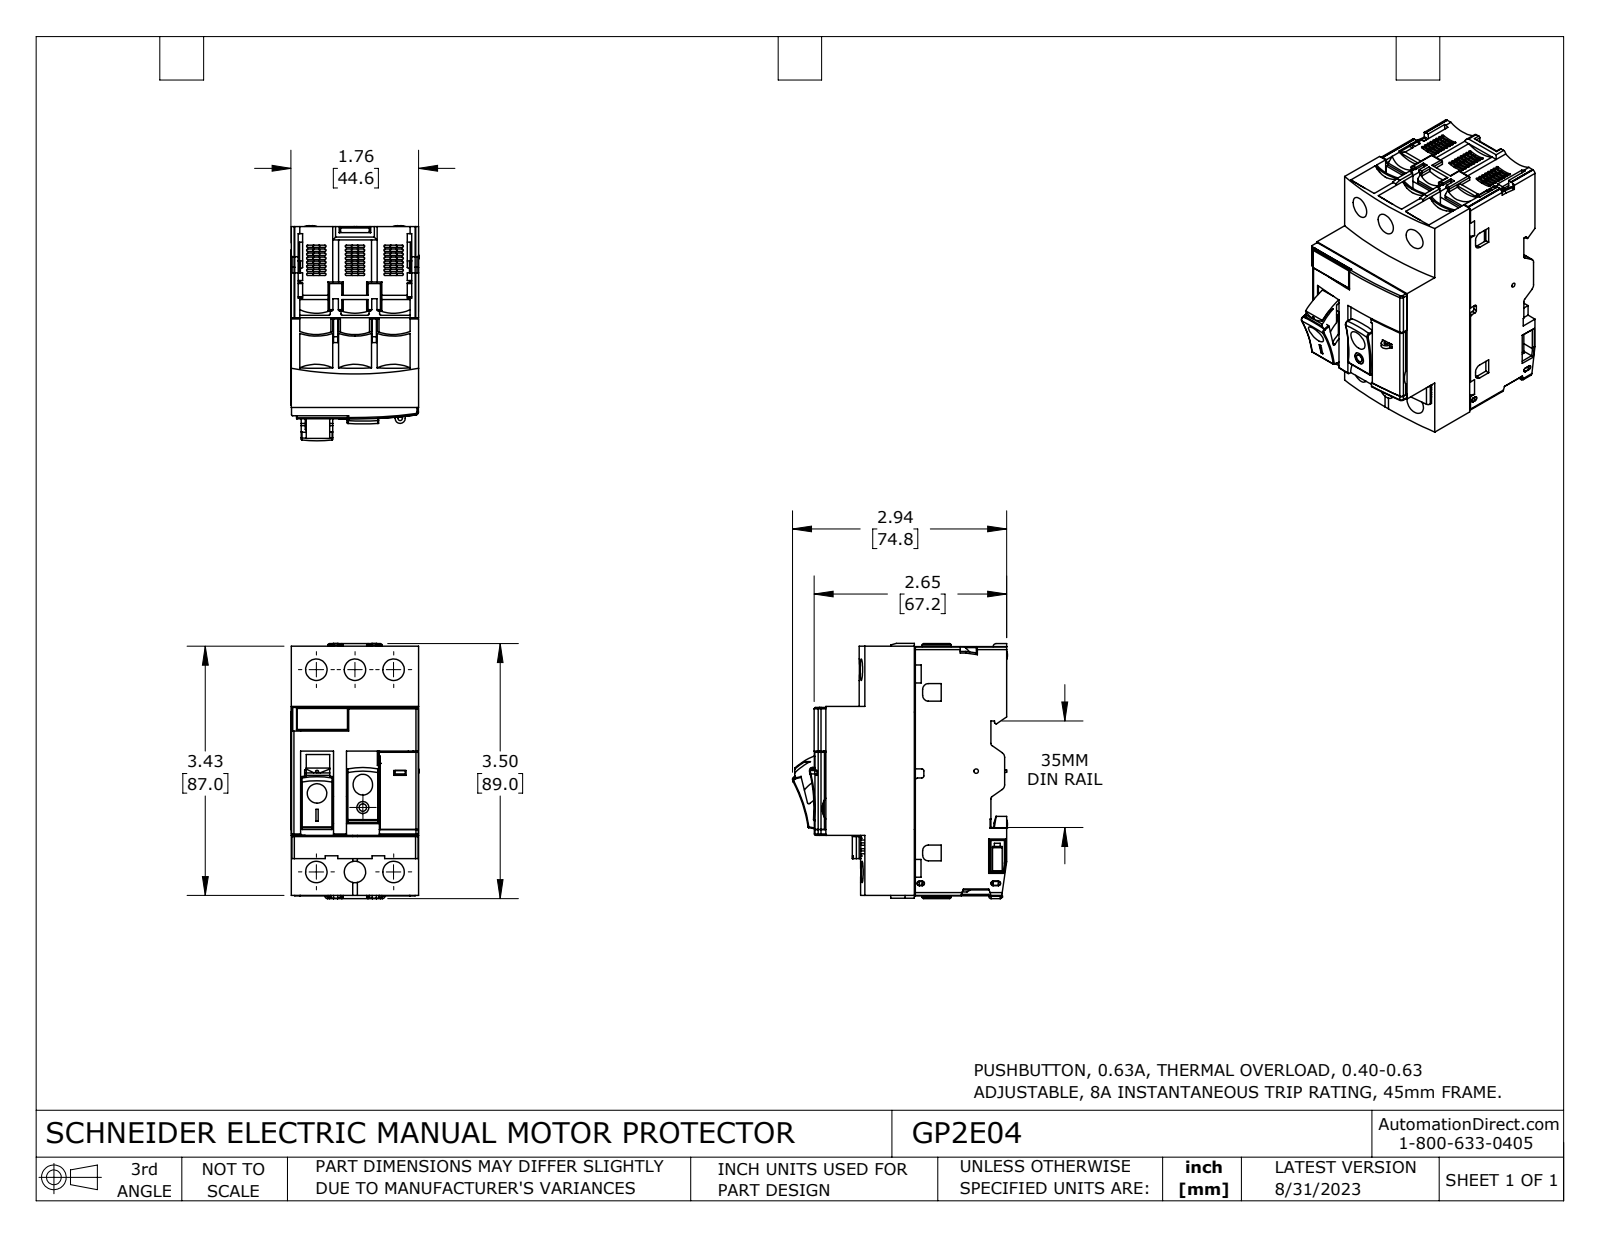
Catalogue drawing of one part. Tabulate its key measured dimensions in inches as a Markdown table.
| quantity | value |
| --- | --- |
| part name | GP2E04 |
| STEP written by | SolidWorks 2021 (CONFIG_CONTROL_DESIGN) |
| units | inches |
| bodies | 15 solids, 2269 faces (1521 planar, 657 cylindrical, 91 other) |
| overall size | 3.508 × 2.957 × 1.764 |
| volume | 11.58 in³ |
| surface area | 98.93 in² |
| round holes (diameter × count) | 0.295 × 6, 0.197 × 5, 0.059 × 2, 0.157 × 1, 0.165 × 1, 0.315 × 1, 0.327 × 1, 0.335 × 1, 0.343 × 1 |
| round bosses / shafts (diameter × count) | 0.244 × 2, 0.118 × 2, 0.382 × 1, 0.102 × 1, 0.047 × 1 |
| partial cylindrical surfaces (radius × count) | 0.016 × 104, 0.02 × 47, 0.039 × 16, 0.01 × 12, 0.012 × 12, 0.031 × 12, 0.059 × 8, 0.004 × 6 |
| main face-to-face distances | 1.752, 0.531, 0.115, 1.233, 1.756, 0.059, 1.637, 0.581, 1.053, 1.171 |
| hole center spacings | 0.531, 2.83, 2.779, 0.346, 0.402, 0.546, 0.671, 0.726 |
